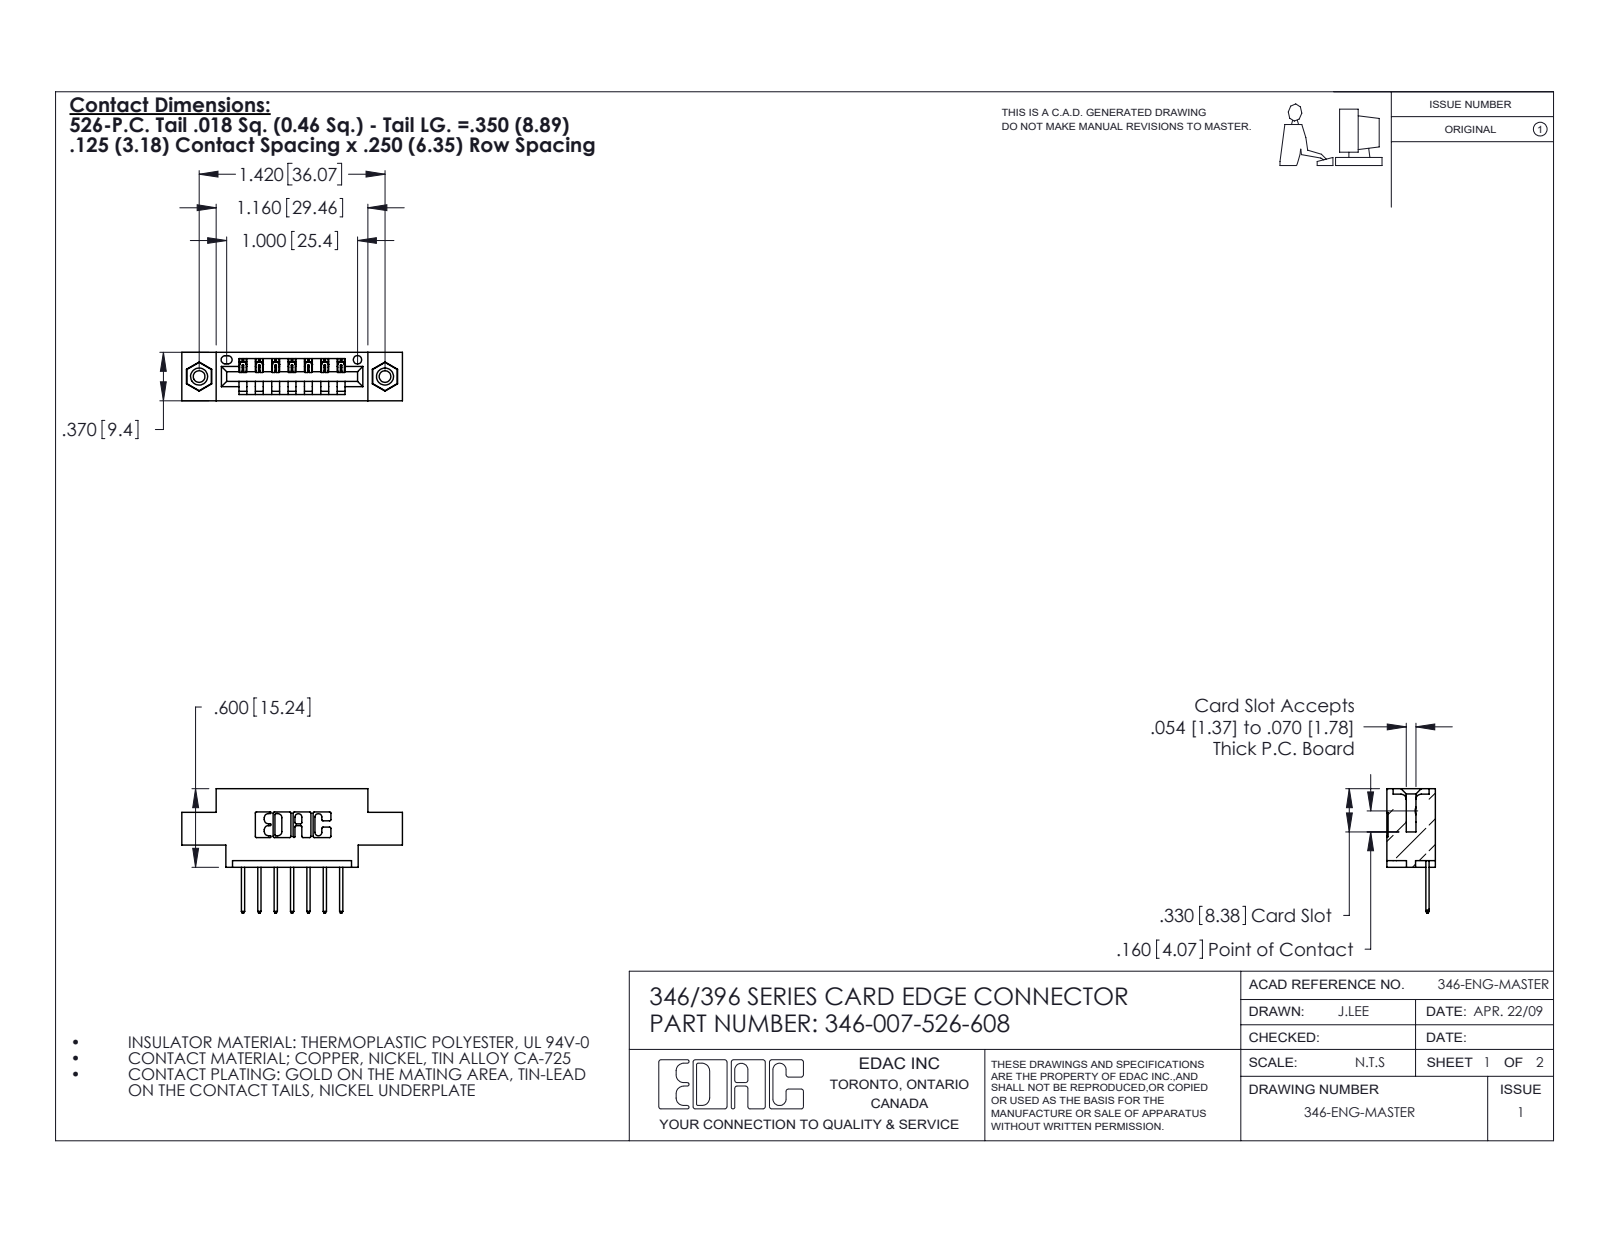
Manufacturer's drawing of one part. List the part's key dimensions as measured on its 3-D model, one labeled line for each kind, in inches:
Part name (STEP PRODUCT): 345-292-001_345-293-126; 345-250-001_345-250-003-102; 346-007-526-608; 346 Part_0.170 Offset - 0.156 Dia-TI
STEP written by: SolidWorks 2020 (CONFIG_CONTROL_DESIGN)
Units: inches
Bodies: 10 solids, 592 faces (392 planar, 184 cylindrical, 16 other)
Overall size (bounding box): 1.685 × 0.95 × 0.37
Volume: 0.225 in³ · Surface area: 6.833 in²
Round holes (diameter × count): ⌀0.089 ×2, ⌀0.125 ×2, ⌀0.156 ×2, ⌀0.064 ×1
Round bosses / shafts (diameter × count): ⌀0.155 ×2
Partial cylindrical surfaces — rounded edges, fillets, slot ends (radius × count): R0.01 ×22, R0.006 ×14, R0.01 ×14, R0.007 ×6, R0.031 ×6, R0.026 ×3, R0.031 ×2, R0.04 ×2
Main face-to-face distances: 0.25, 0.37, 0.048, 0.322, 0.222, 0.148, 0.1, 0.174, 0.072, 0.298
Hole centre spacings: 0.246, 1.217, 1.42
